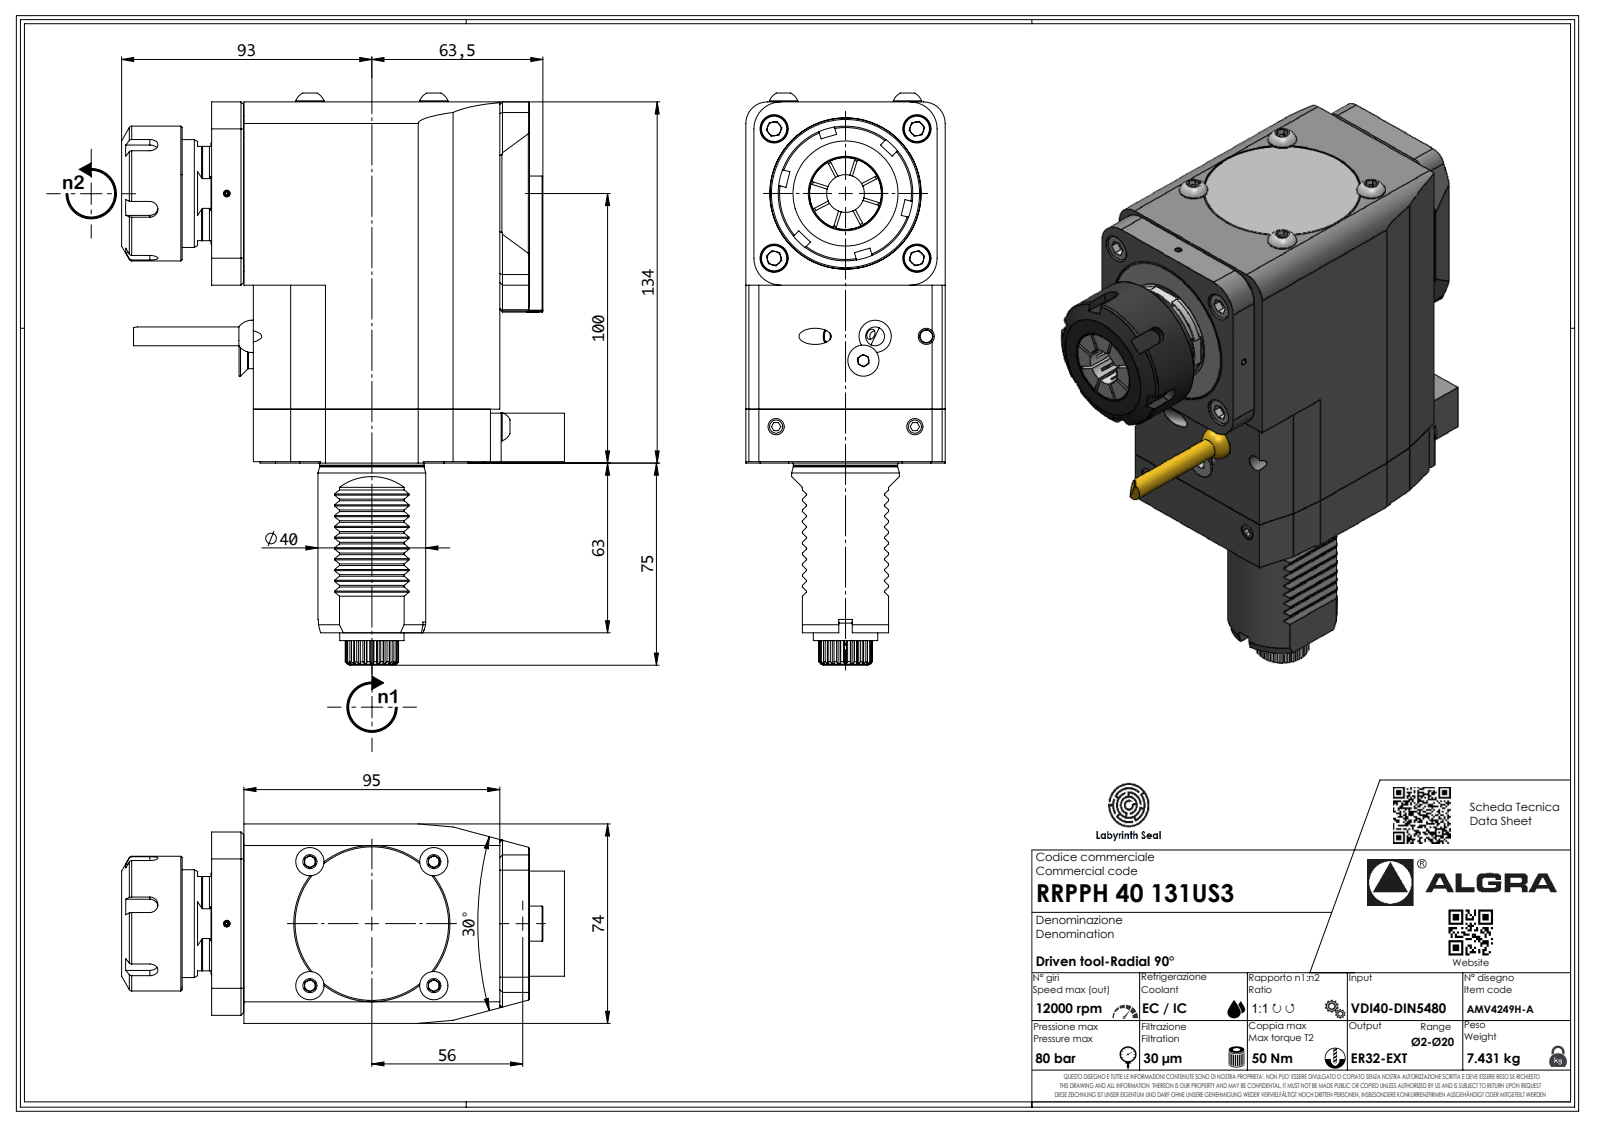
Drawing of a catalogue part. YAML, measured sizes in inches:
part_name: "RRPPH40131US3"
step_written_by: "SolidWorks 2023 (AUTOMOTIVE_DESIGN)"
units: inches
bodies: {solids: 4, faces: 719, planar: 471, cylindrical: 119, other: 129}
overall_size: [8.228, 6.473, 2.913]
volume: 71.89
surface_area: 148.6
round_holes:
  - {diameter: 0.551, count: 4}
  - {diameter: 0.083, count: 1}
  - {diameter: 1.197, count: 1}
round_bosses_or_shafts:
  - {diameter: 1.575, count: 2}
  - {diameter: 1.969, count: 1}
  - {diameter: 1.524, count: 1}
  - {diameter: 1.054, count: 1}
  - {diameter: 0.941, count: 1}
  - {diameter: 0.251, count: 1}
  - {diameter: 0.067, count: 1}
partial_cylinders:
  - {radius: 0.012, count: 20}
  - {radius: 0.013, count: 7}
  - {radius: 0.02, count: 7}
  - {radius: 0.118, count: 7}
  - {radius: 0.146, count: 7}
  - {radius: 0.236, count: 4}
  - {radius: 0.394, count: 4}
  - {radius: 0.315, count: 2}
face_to_face_distances: [2.913, 3.602, 0.413, 0.138, 4.016, 4.626, 0.61, 4.213, 5.276, 2.677]
hole_center_spacings: [1.648, 2.126, 2.52, 3.297]
